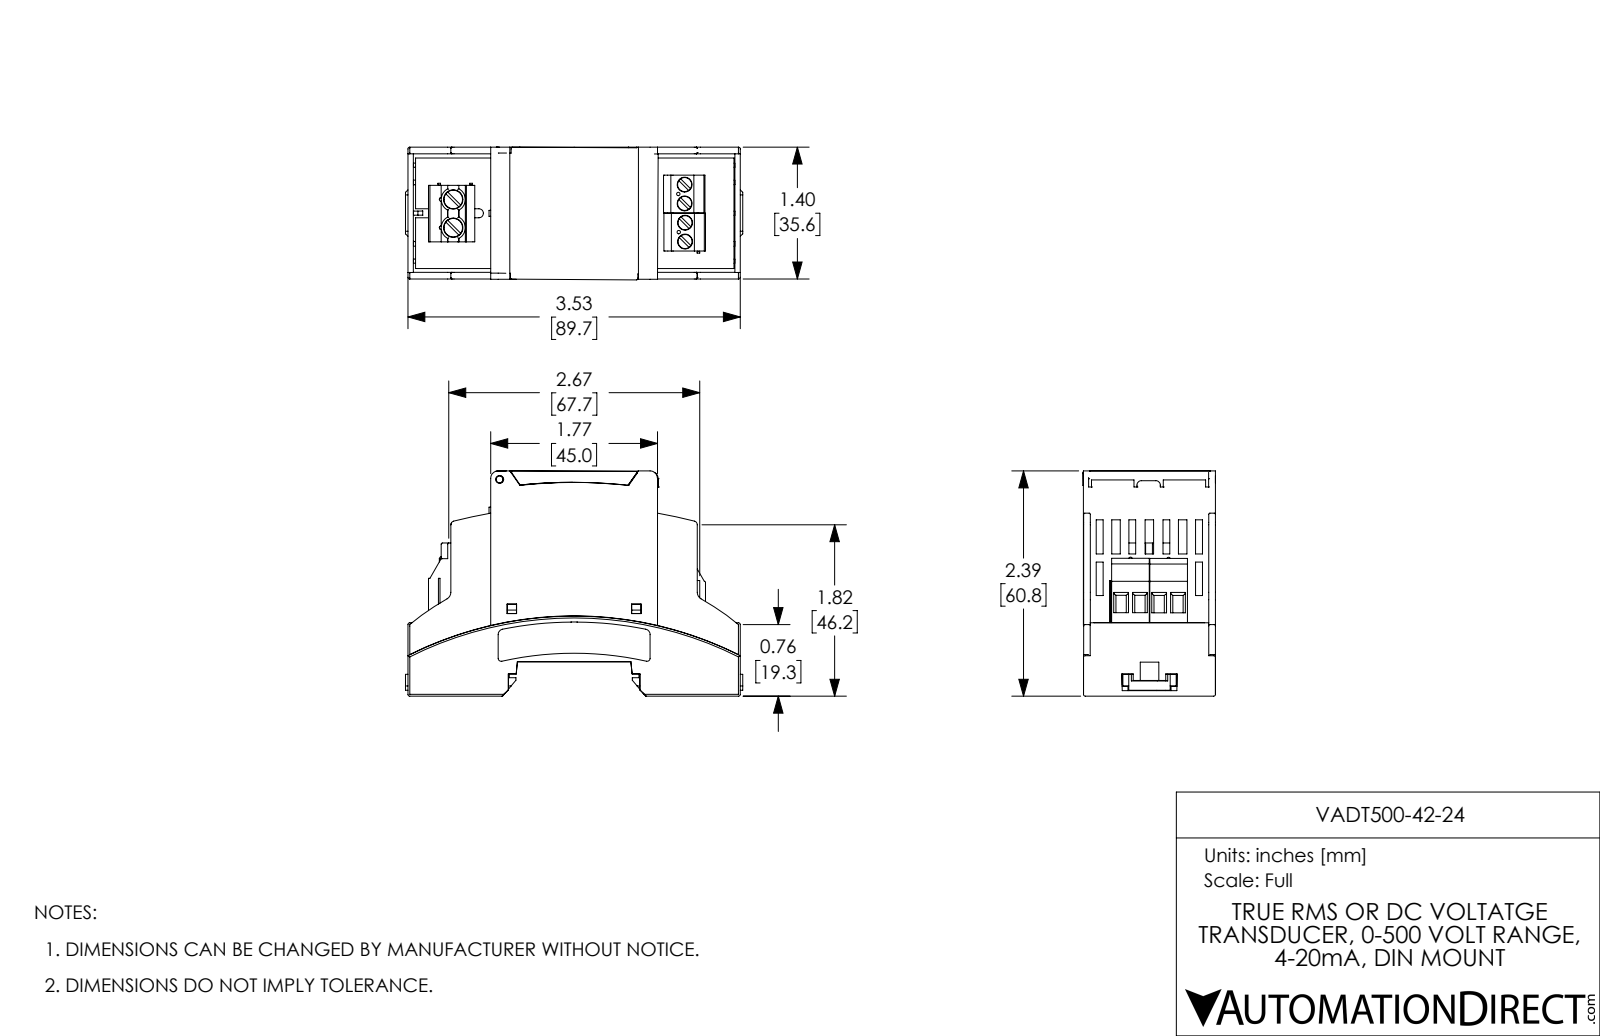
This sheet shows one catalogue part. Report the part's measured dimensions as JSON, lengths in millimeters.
{"part_name": "VADT500-42-24", "step_written_by": "SolidWorks 2021 (AUTOMOTIVE_DESIGN)", "units": "millimeters", "bodies": {"solids": 7, "faces": 895, "planar": 538, "cylindrical": 166, "other": 191}, "overall_size": [106.8, 58.4, 37.1], "volume_mm3": 52140, "surface_area_mm2": 50570, "round_holes": [[4, 4], [5.2, 2]], "round_bosses_or_shafts": [[1.3, 6], [3.8, 4], [0.5, 3], [5, 2]], "partial_cylinders_radius": [[0.2, 27], [1, 12], [0.5, 11], [0.2, 10], [0.7, 8], [0.3, 6], [0.8, 4], [1, 4]], "face_to_face_distances": [36.4, 1.6, 11.1, 12.7, 32.5, 31.7, 6.8, 17.9, 19.5, 19.6], "hole_center_spacings": [5.1, 10.2, 62.7, 9.5, 15.2, 62.7, 62.7, 63]}
